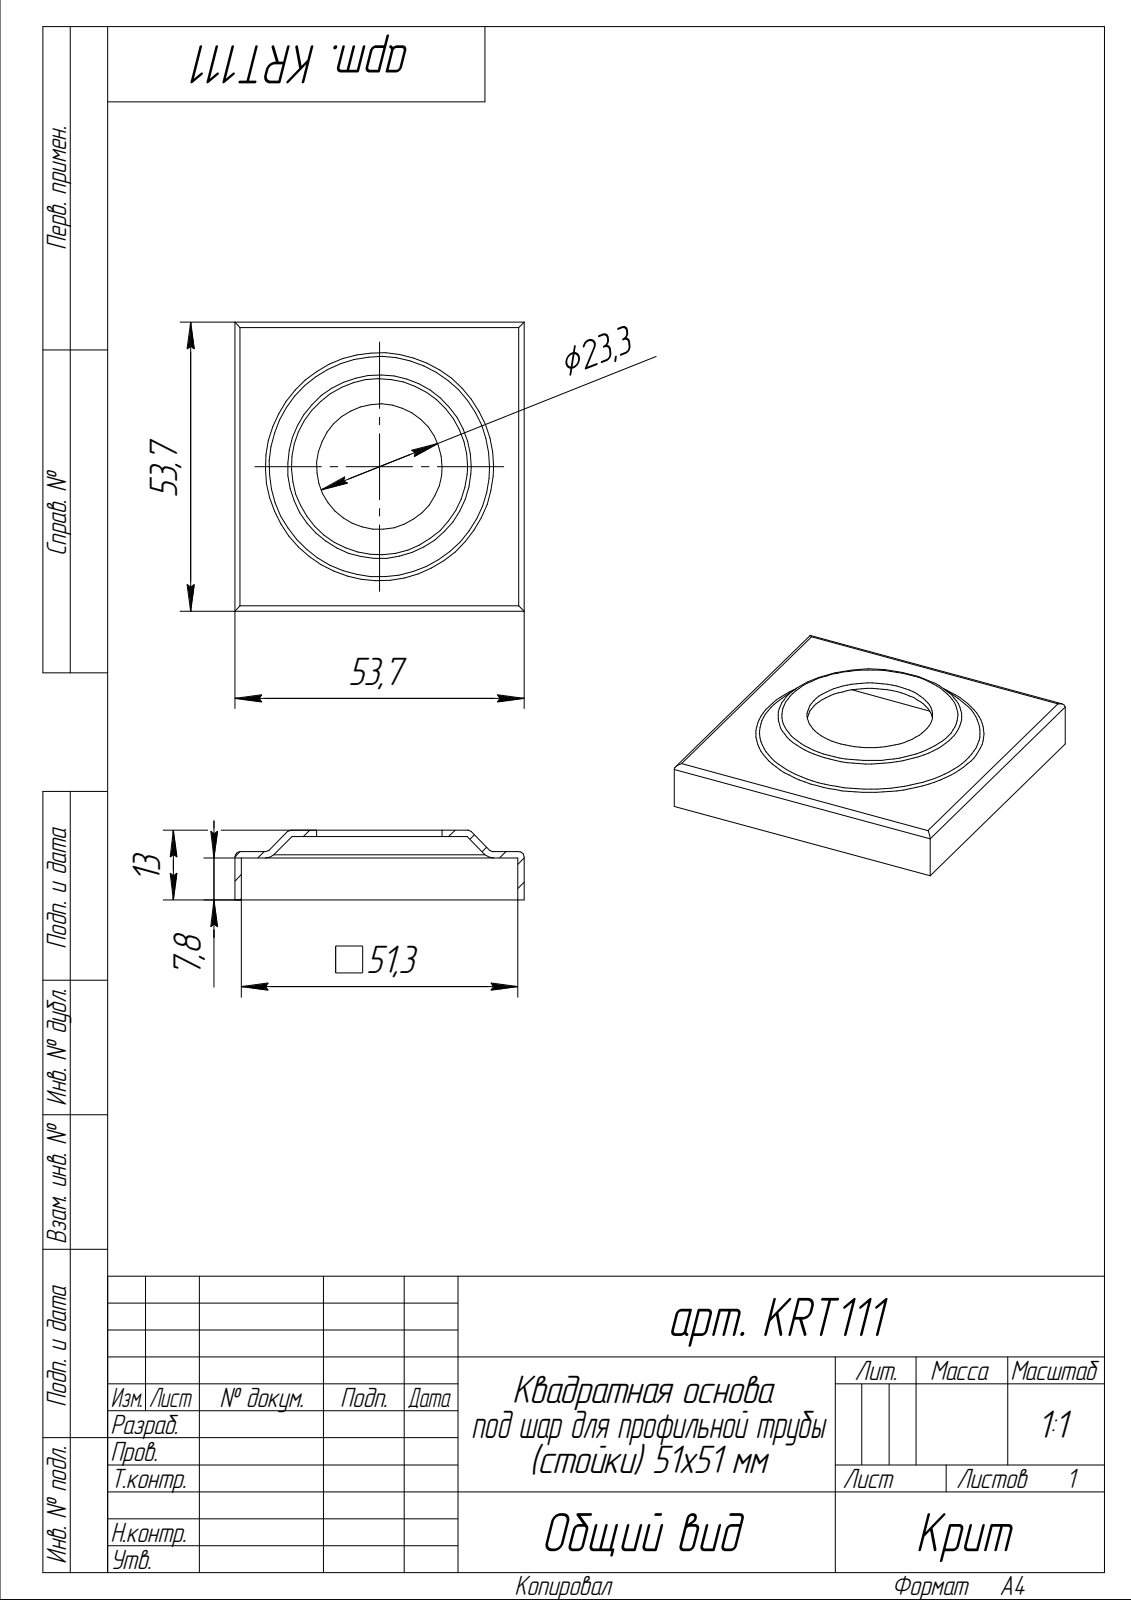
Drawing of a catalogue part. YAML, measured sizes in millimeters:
part_name: "арт. KRT111"
step_written_by: "SolidWorks 2014 (AUTOMOTIVE_DESIGN)"
units: millimeters
bodies: {solids: 1, faces: 29, planar: 13, cylindrical: 6, other: 10}
overall_size: [53.7, 53.7, 13]
volume: 5087
surface_area: 8807
round_holes:
  - {diameter: 23.3, count: 1}
partial_cylinders:
  - {radius: 1, count: 4}
face_to_face_distances: [1.2, 52.5, 53.7, 4, 51.3, 5.2, 2.8, 7.8, 9, 11.8]
